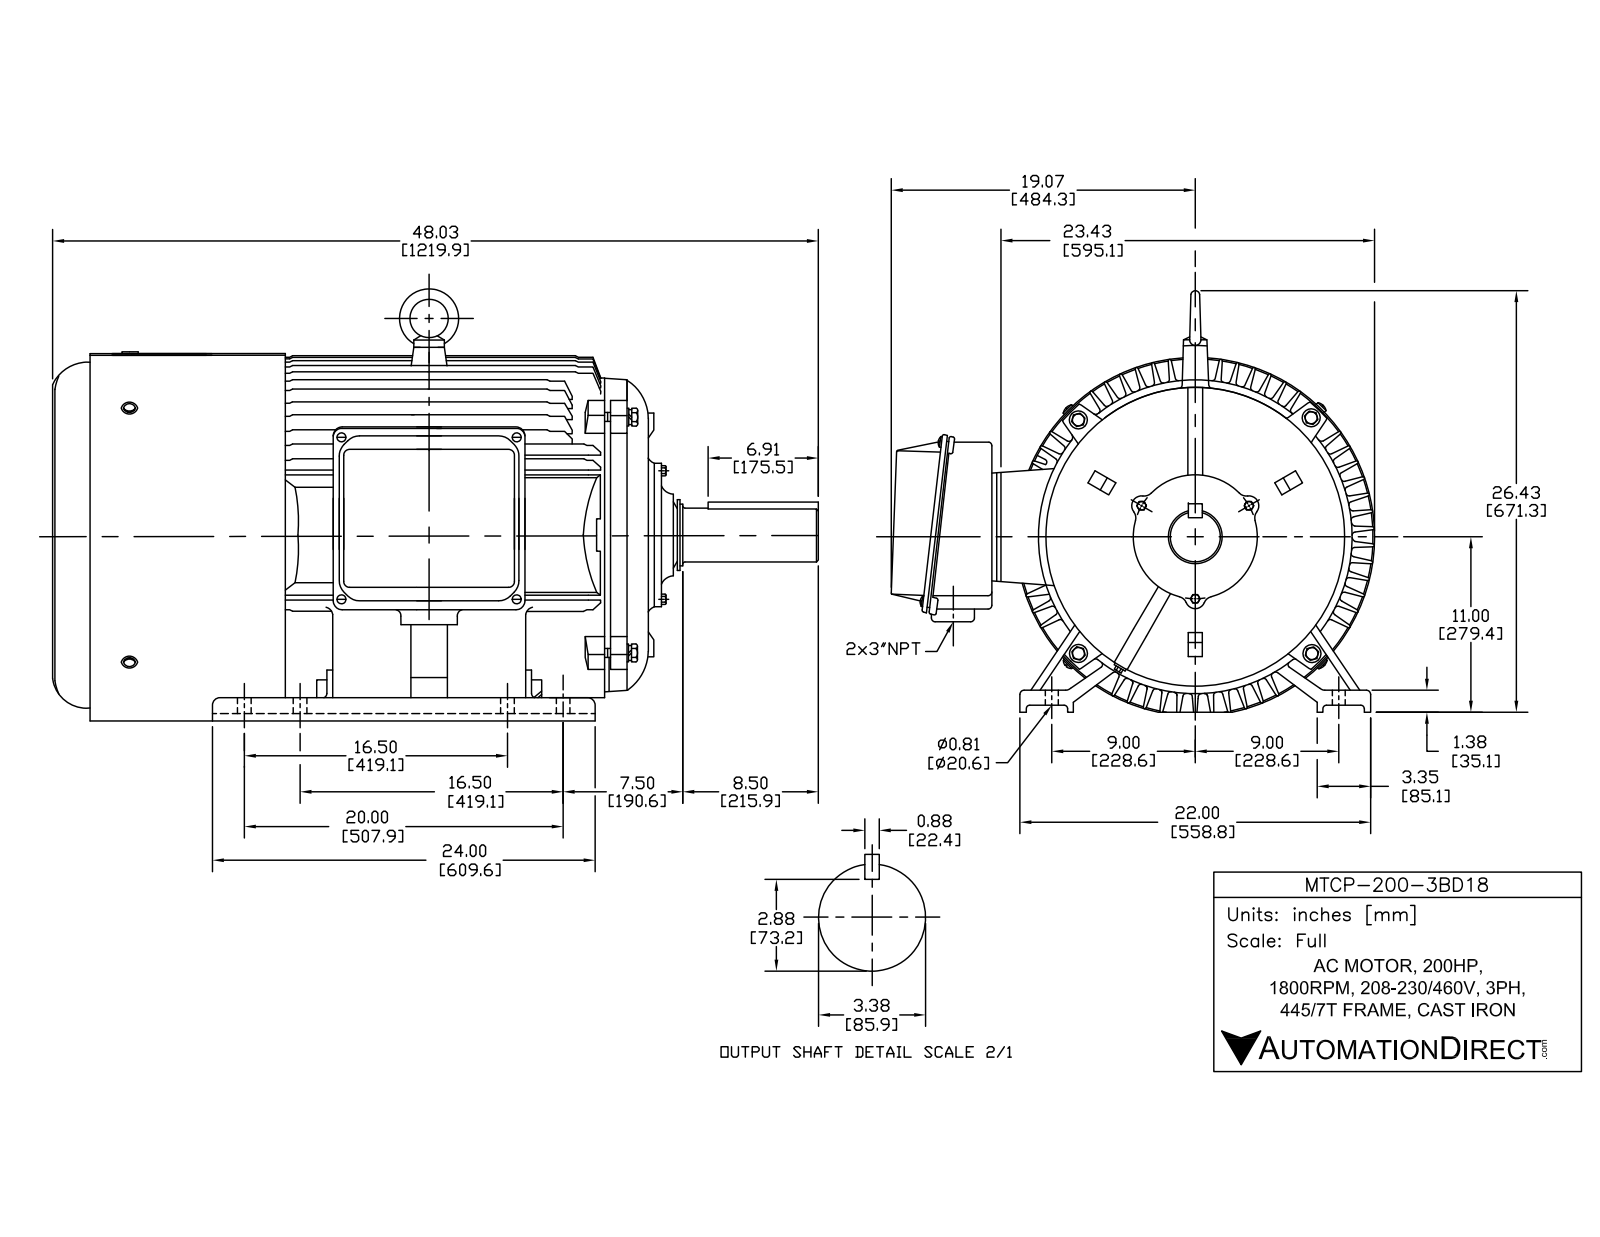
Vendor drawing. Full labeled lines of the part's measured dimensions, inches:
Part name (STEP PRODUCT): hexagon head bolts-full thread gb_GB_FASTENER_BOLT_STBAB A M10X25-N; spring lock washers--normal type gb_GB_FASTENER_WASHER_SW 12; eyebolts gb_GB_FASTENER_SCREWS_FRS M30-N; hex head bolts-full thread grade c gb_GB_FASTENER_BOLT_HHBFTC M8X16-N (+8 more)
STEP written by: SolidWorks 2017 (AUTOMOTIVE_DESIGN)
Units: inches
Bodies: 68 solids, 4228 faces (1205 planar, 1564 cylindrical, 1459 other)
Overall size (bounding box): 47.732 × 30.755 × 27.012
Volume: 2 611 in³ · Surface area: 12 660 in²
Round holes (diameter × count): ⌀0.472 ×20, ⌀0.268 ×8, ⌀0.335 ×8, ⌀0.827 ×8, ⌀0.081 ×4, ⌀0.236 ×4, ⌀0.331 ×4, ⌀0.342 ×4, ⌀0.354 ×4, ⌀0.394 ×4, ⌀0.402 ×4, ⌀0.508 ×4
Round bosses / shafts (diameter × count): ⌀0.394 ×16, ⌀0.945 ×4, ⌀0.752 ×4, ⌀0.63 ×4, ⌀0.507 ×4, ⌀0.472 ×4, ⌀0.315 ×4, ⌀22.992 ×1
Partial cylindrical surfaces — rounded edges, fillets, slot ends (radius × count): R0.039 ×254, R0.197 ×93, R0.118 ×90, R0.079 ×42, R0.236 ×37, R0.354 ×36, R0.394 ×25, R0.03 ×24
Main face-to-face distances: 0.236, 0.079, 0.354, 0.579, 0.787, 1.469, 0.984, 37.358, 37.28, 1.575
Hole centre spacings: 5.118, 3.445, 4.429, 6.837, 4.028, 10.551, 0.984, 3.5
